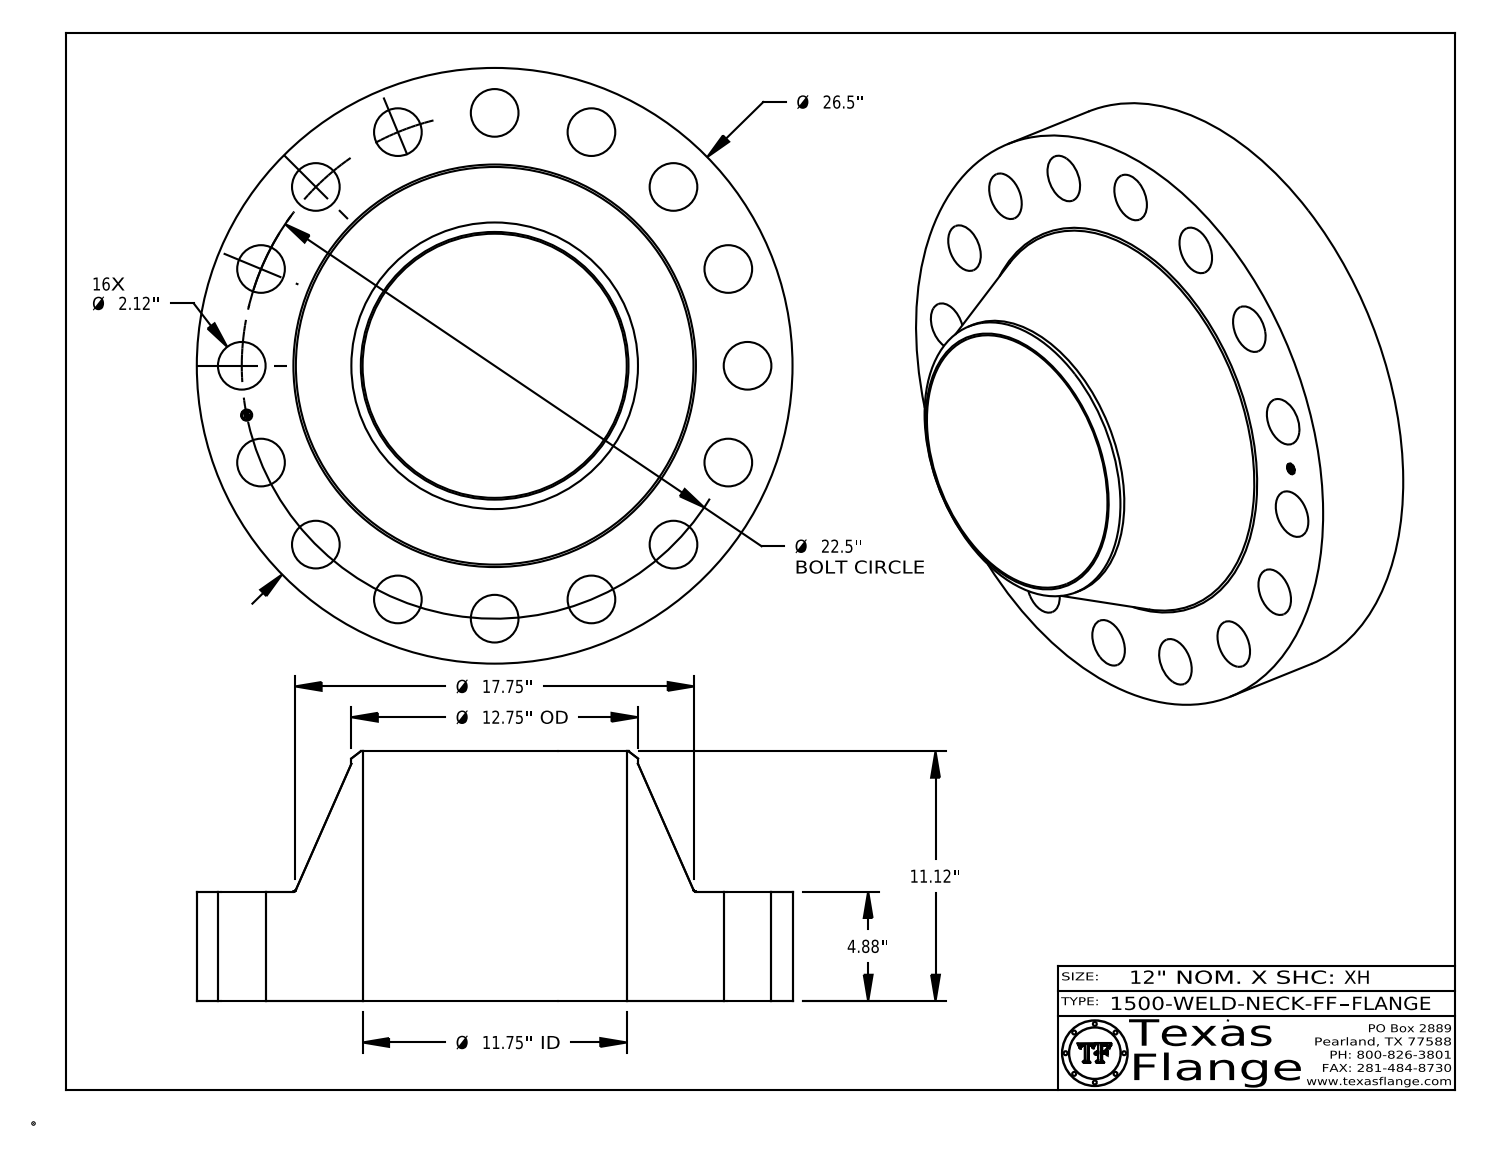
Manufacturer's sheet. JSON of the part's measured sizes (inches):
{"part_name": "1500-WELD-NECK-FF", "step_written_by": "CATIA V5 STEP AP214 (AUTOMOTIVE_DESIGN)", "units": "inches", "bodies": {"solids": 1, "faces": 432, "planar": 368, "cylindrical": 58, "other": 6}, "overall_size": [26.5, 26.5, 11.12], "volume_in3": 2326, "surface_area_in2": 2300, "round_holes": [[2.12, 16], [0.495, 1], [11.75, 1]], "round_bosses_or_shafts": [[0.03, 8], [26.5, 1], [12.75, 1], [0.39, 1]], "face_to_face_distances": [4.88, 11.12, 6.24, 4.865, 0.015, 6.255, 0.148, 0.145, 0.027, 0.096], "hole_center_spacings": [12.5, 20.787, 22.068, 11.25, 8.611, 15.91, 4.389, 4.39]}
